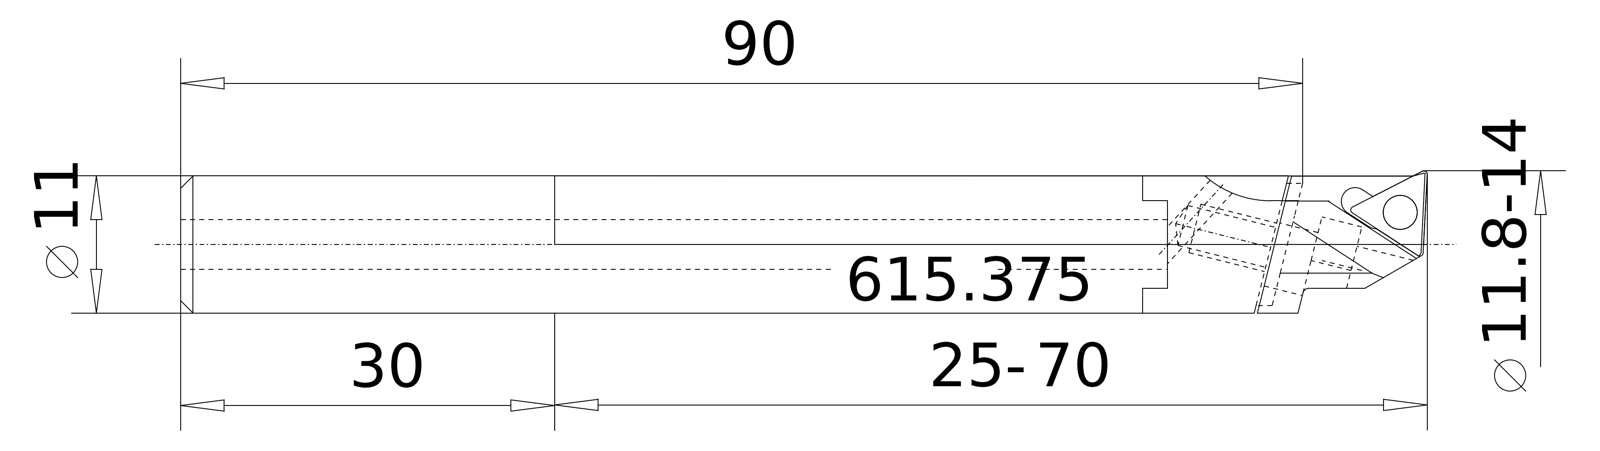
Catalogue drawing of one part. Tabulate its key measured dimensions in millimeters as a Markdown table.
| quantity | value |
| --- | --- |
| part name | Fase2 |
| STEP written by | ACIS (automotive_design) |
| units | millimeters |
| bodies | 1 solid, 53 faces (18 planar, 25 cylindrical, 10 other) |
| overall size | 89.82 × 11 × 11 |
| volume | 7 667 mm³ |
| surface area | 4 092 mm² |
| round holes (diameter × count) | 1.5 × 1, 2 × 1, 2.05 × 1, 3 × 1, 3.3 × 1, 4.5 × 1 |
| round bosses / shafts (diameter × count) | 11 × 1 |
| partial cylindrical surfaces (radius × count) | 2 × 1, 8 × 1 |
| main face-to-face distances | 1.25, 2.5, 5, 5.48, 78, 5.5, 6.25, 7.5, 6.26, 7.51 |
| hole center spacings | 0.4, 4.12, 4.51 |
